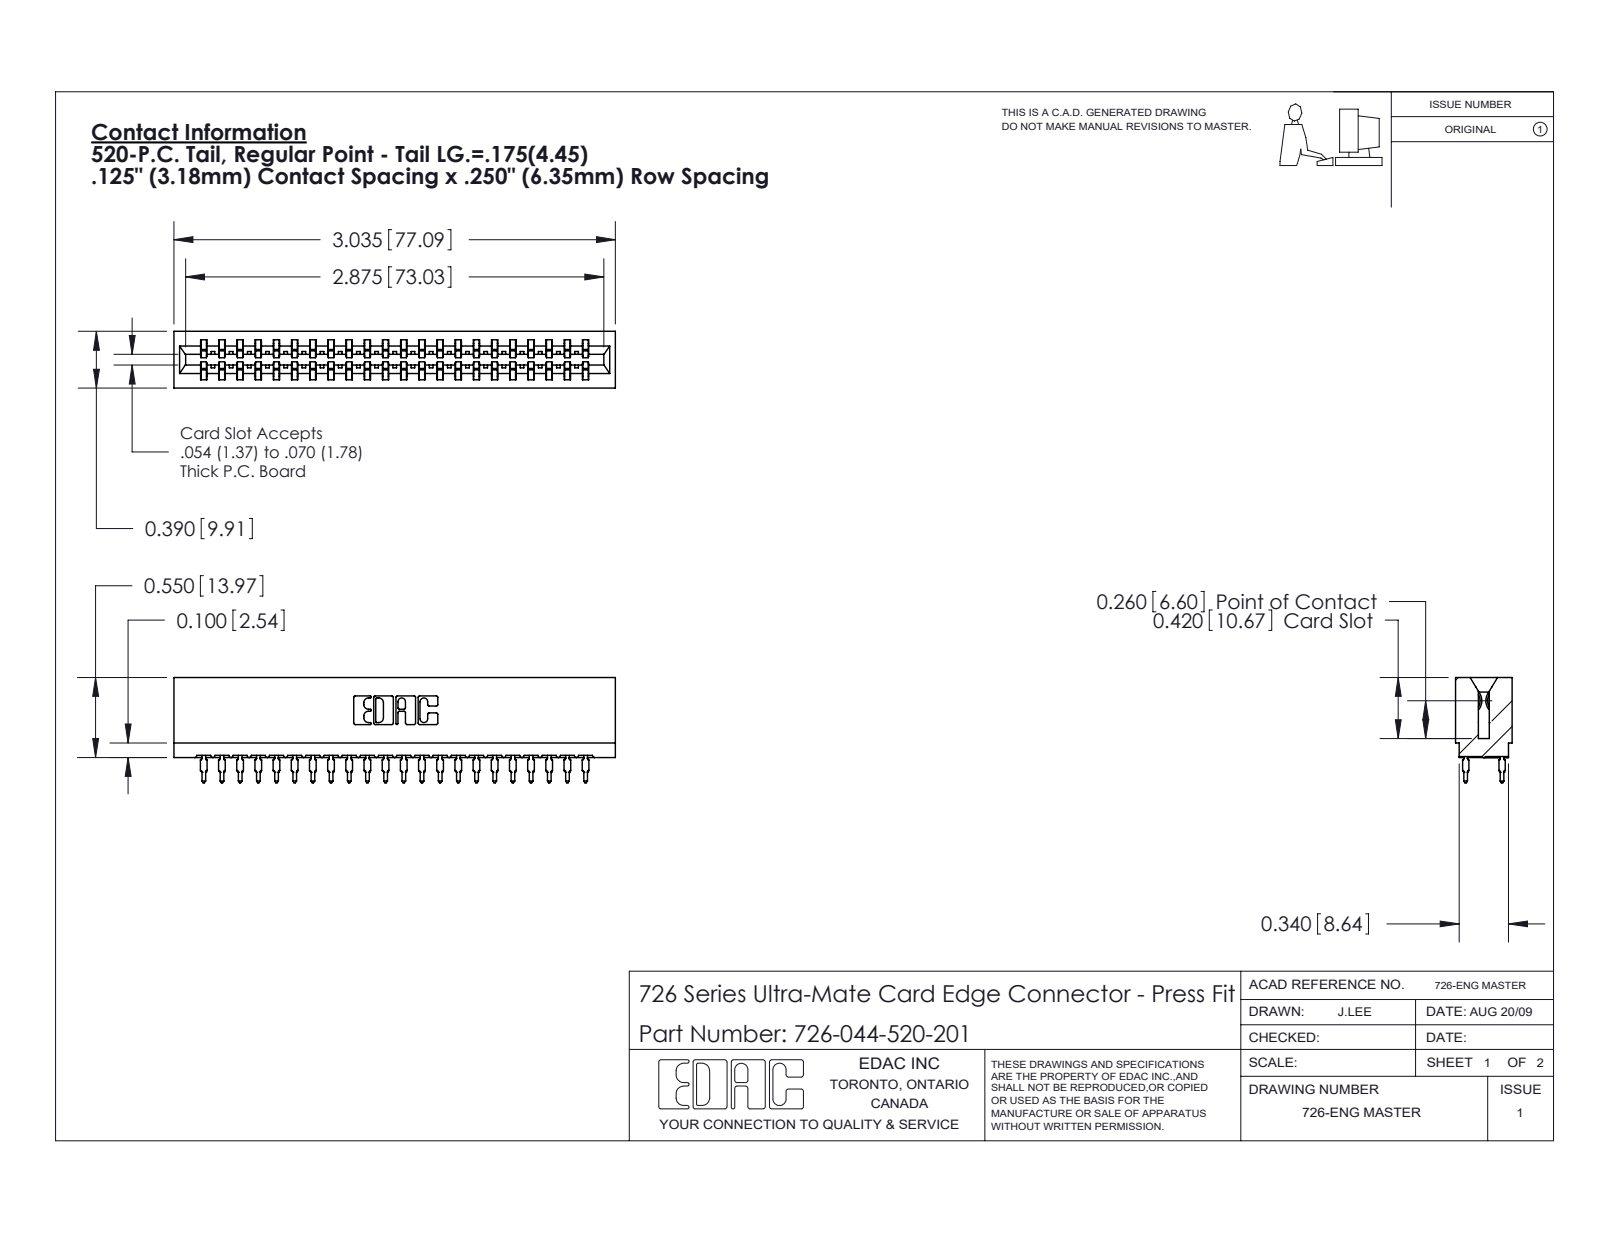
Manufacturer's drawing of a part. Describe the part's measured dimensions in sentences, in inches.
The part is named "726 Part_.515 Slot Depth - 01; 746-292-001_520; 726-044-520-201". Its 3-D file was written by "SolidWorks 2020 (CONFIG_CONTROL_DESIGN)". It is 45 solids with 4035 faces: 2079 planar, 812 cylindrical and 1144 other. Overall it measures 3.035 by 0.724 by 0.39 inches. Its volume is 0.437 cubic inches and its surface area 17.66 square inches. Partial cylindrical surfaces (rounded edges, fillets, slot ends): 88 of radius 0.021, 23 of radius 0.015, 22 of radius 0.01, 8 of radius 0.005, 8 of radius 0.011, 6 of radius 0.007, 6 of radius 0.031, 3 of radius 0.026. The main face-to-face distances are 0.057, 0.333, 0.39, 0.025, 0.307, 0.25, 0.083, 0.275, 0.042, 1.25.
